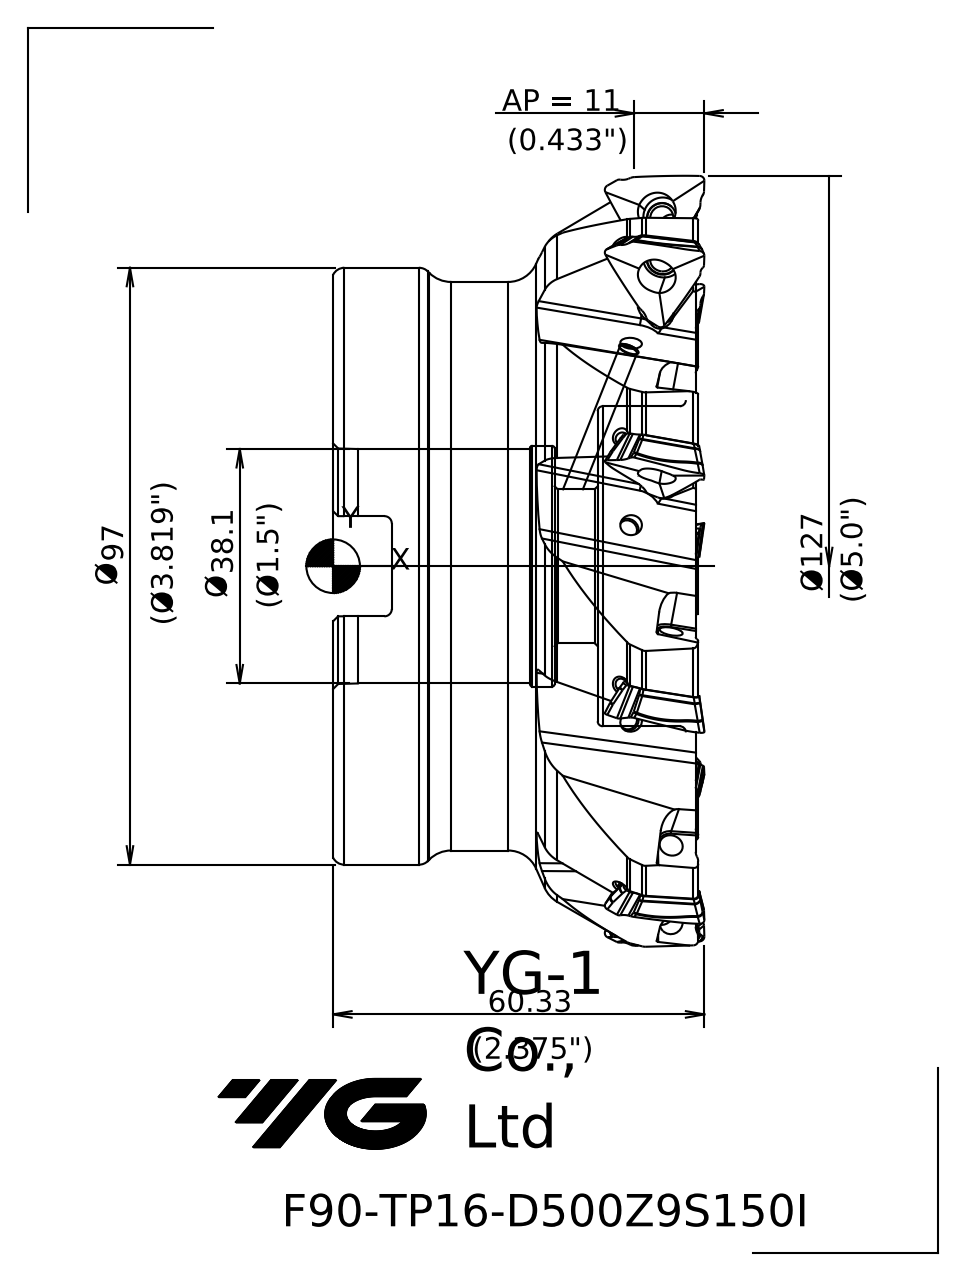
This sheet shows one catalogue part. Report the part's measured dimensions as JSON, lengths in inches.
{"part_name": "1022C79461C3qzun", "step_written_by": "SIEMENS PLM Software NX 10.0 (AP203_CONFIGURATION_CONTROLLED_3D_DESIGN_OF_MECHANICAL_PARTS_AND_ASSEMBLIES_MIM_LF)", "units": "inches", "bodies": {"solids": 1, "faces": 78, "planar": 18, "cylindrical": 10, "other": 50}, "overall_size": [5.006, 5.006, 2.375], "volume_in3": 25.77, "surface_area_in2": 101.7, "round_holes": [[0.984, 1], [1.5, 1], [1.539, 1], [2.047, 1]], "round_bosses_or_shafts": [[3.819, 1], [3.638, 1]], "partial_cylinders_radius": [[0.047, 2]], "face_to_face_distances": [2.32, 0.063, 2.257, 0.627, 0.564, 1.693, 1.944, 1.881, 1.317, 0.376]}
